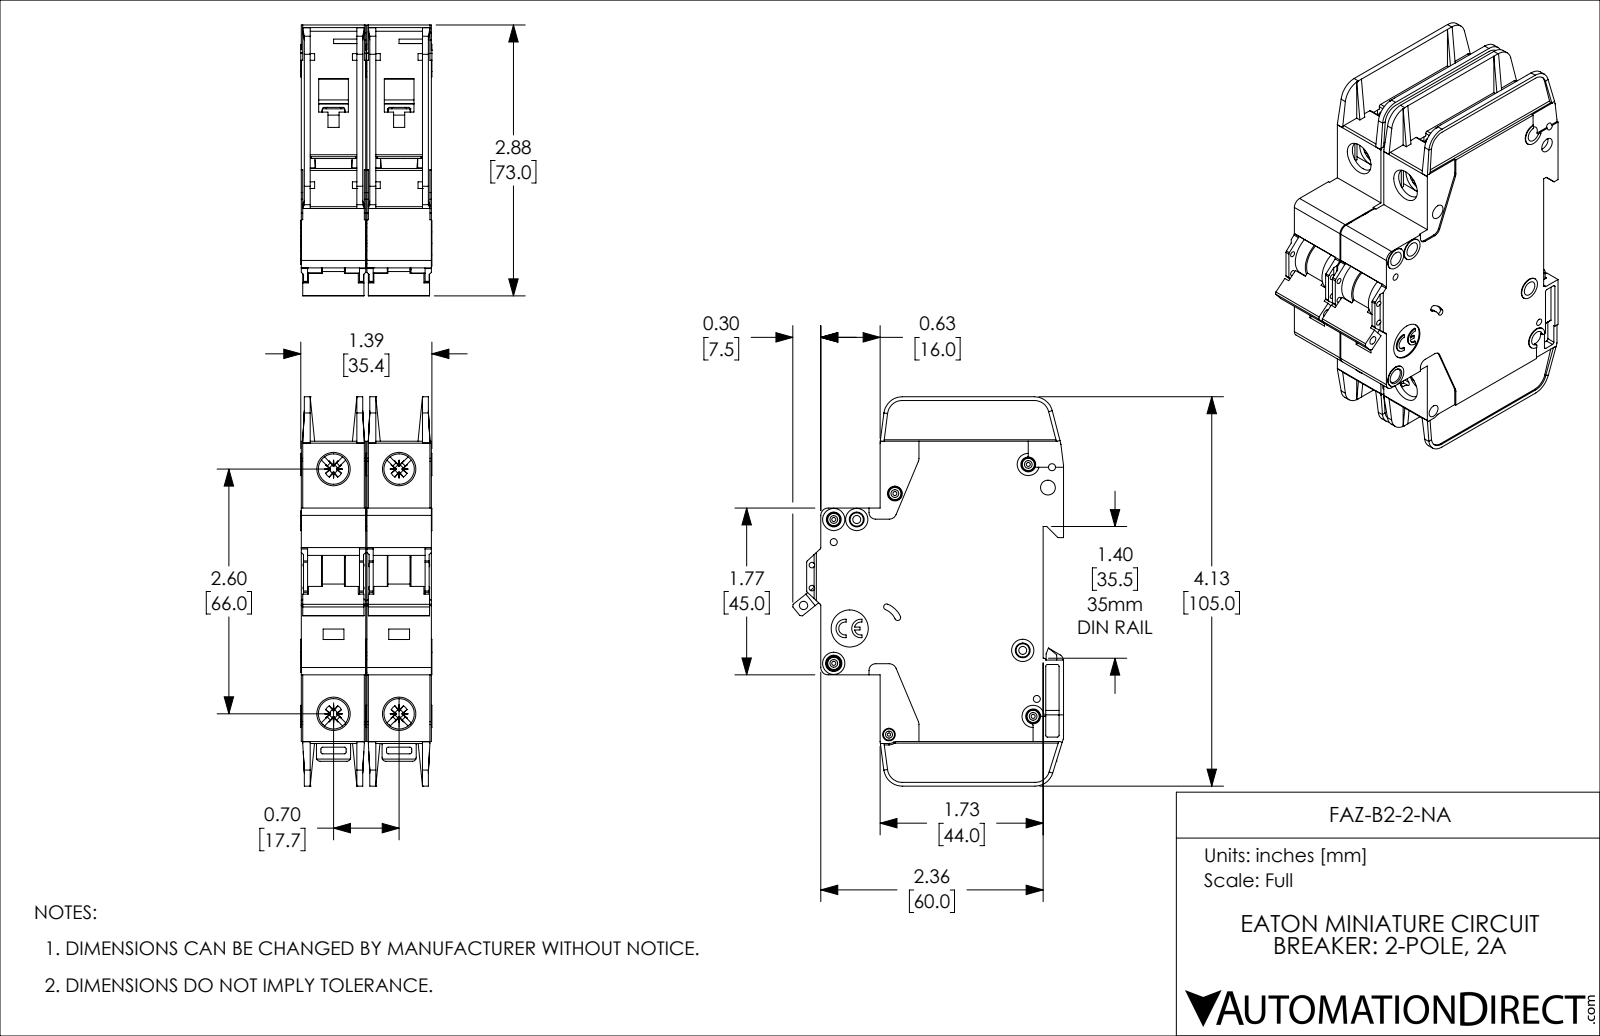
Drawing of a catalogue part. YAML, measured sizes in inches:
part_name: "FAZ-B2-2-NA"
step_written_by: "SolidWorks 2019 (AUTOMOTIVE_DESIGN)"
units: inches
bodies: {solids: 2, faces: 2254, planar: 1342, cylindrical: 714, other: 198}
overall_size: [4.134, 2.876, 1.394]
volume: 9.365
surface_area: 82.01
round_holes:
  - {diameter: 0.157, count: 8}
  - {diameter: 0.043, count: 5}
  - {diameter: 0.075, count: 4}
  - {diameter: 0.323, count: 4}
  - {diameter: 0.059, count: 2}
  - {diameter: 0.085, count: 2}
  - {diameter: 0.035, count: 1}
  - {diameter: 0.089, count: 1}
  - {diameter: 0.098, count: 1}
  - {diameter: 0.134, count: 1}
  - {diameter: 0.394, count: 1}
round_bosses_or_shafts:
  - {diameter: 0.13, count: 5}
  - {diameter: 0.236, count: 4}
  - {diameter: 0.118, count: 3}
  - {diameter: 0.098, count: 2}
partial_cylinders:
  - {radius: 0.02, count: 57}
  - {radius: 0.016, count: 20}
  - {radius: 0.039, count: 14}
  - {radius: 0.079, count: 10}
  - {radius: 0.043, count: 8}
  - {radius: 0.008, count: 5}
  - {radius: 0.197, count: 5}
  - {radius: 0.01, count: 4}
face_to_face_distances: [0.697, 0.047, 0.685, 0.591, 0.094, 0.638, 0.543, 1.382, 0.744, 0.65]
hole_center_spacings: [0.244, 0.537, 0.697, 0.87, 2.598, 2.69, 0.189, 0.199]
